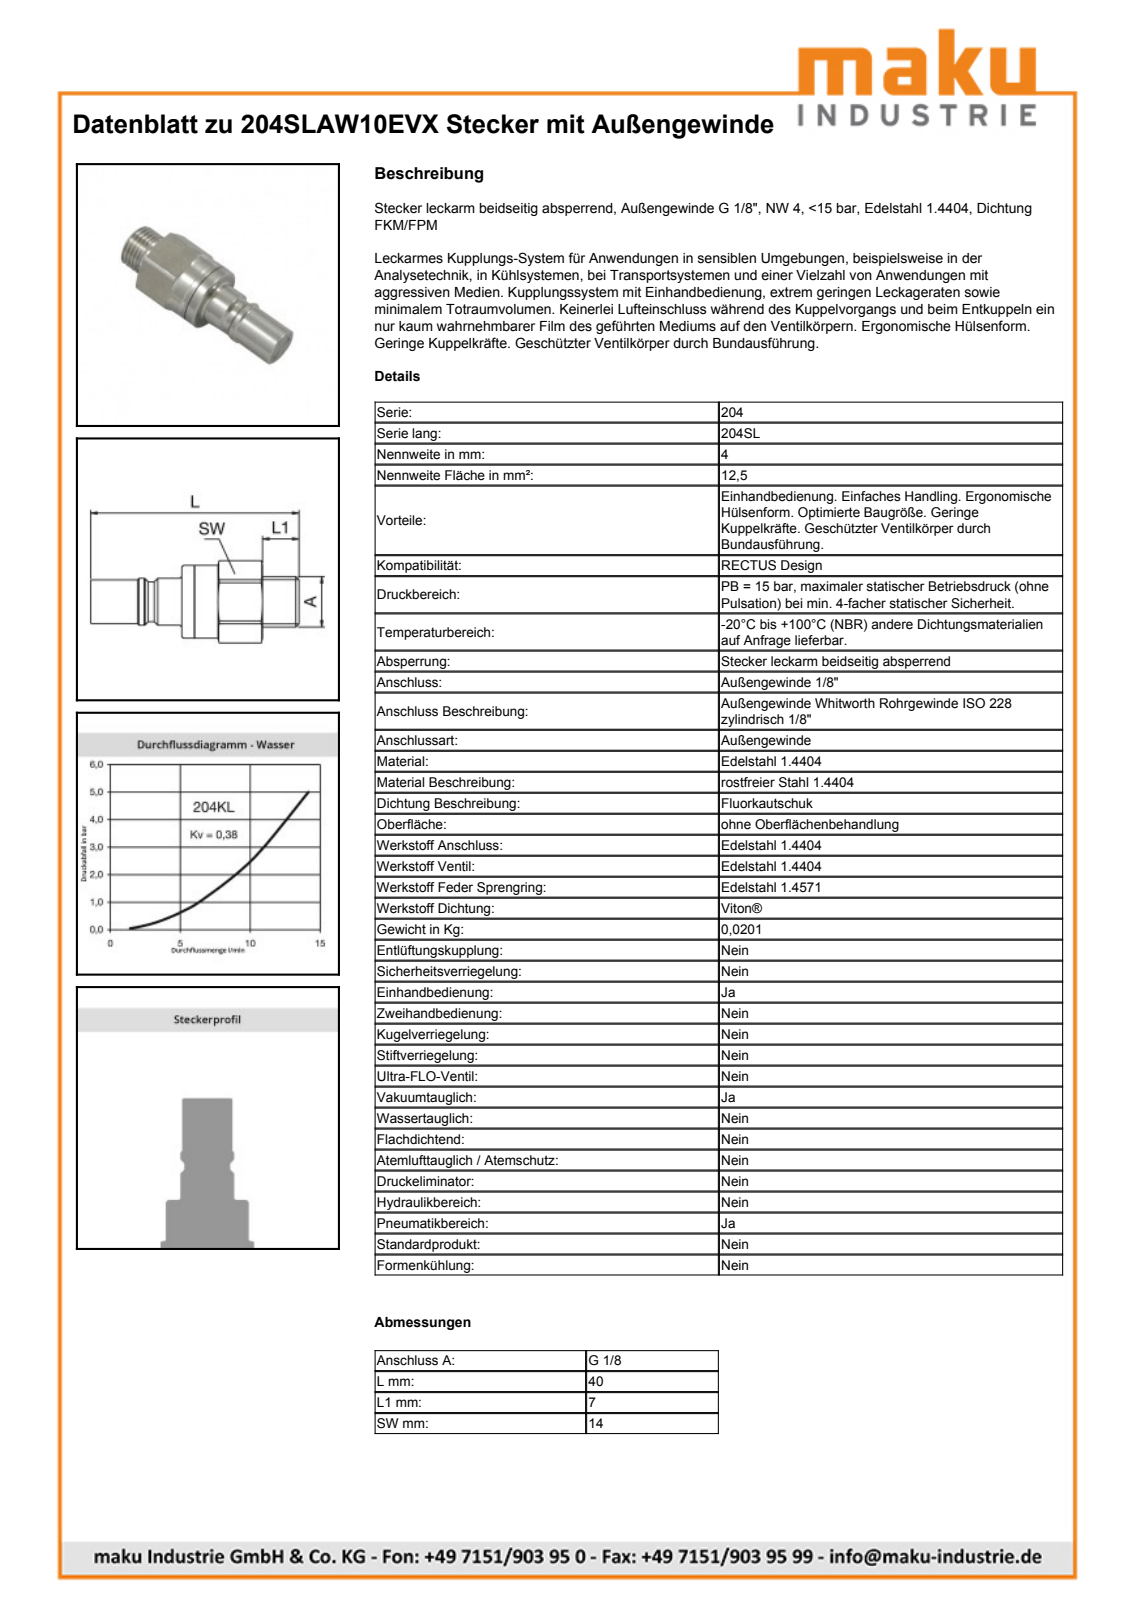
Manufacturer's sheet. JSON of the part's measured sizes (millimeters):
{"part_name": "D111058", "step_written_by": "Autodesk Inventor 2013 (AUTOMOTIVE_DESIGN)", "units": "millimeters", "bodies": {"solids": 1, "faces": 76, "planar": 16, "cylindrical": 23, "other": 37}, "overall_size": [39.9, 15.8, 14], "volume_mm3": 3533, "surface_area_mm2": 2945, "round_holes": [[7.6, 1], [9.4, 1], [10.45, 1], [12, 1]], "round_bosses_or_shafts": [[14, 1], [11.4, 1], [10.35, 1], [9.73, 1], [9, 1], [8.4, 1], [6.67, 1]], "partial_cylinders_radius": [[7.9, 1]], "face_to_face_distances": [14, 7, 15.4, 22.4, 13.4, 2, 9, 17.5, 30.9, 32.9]}
